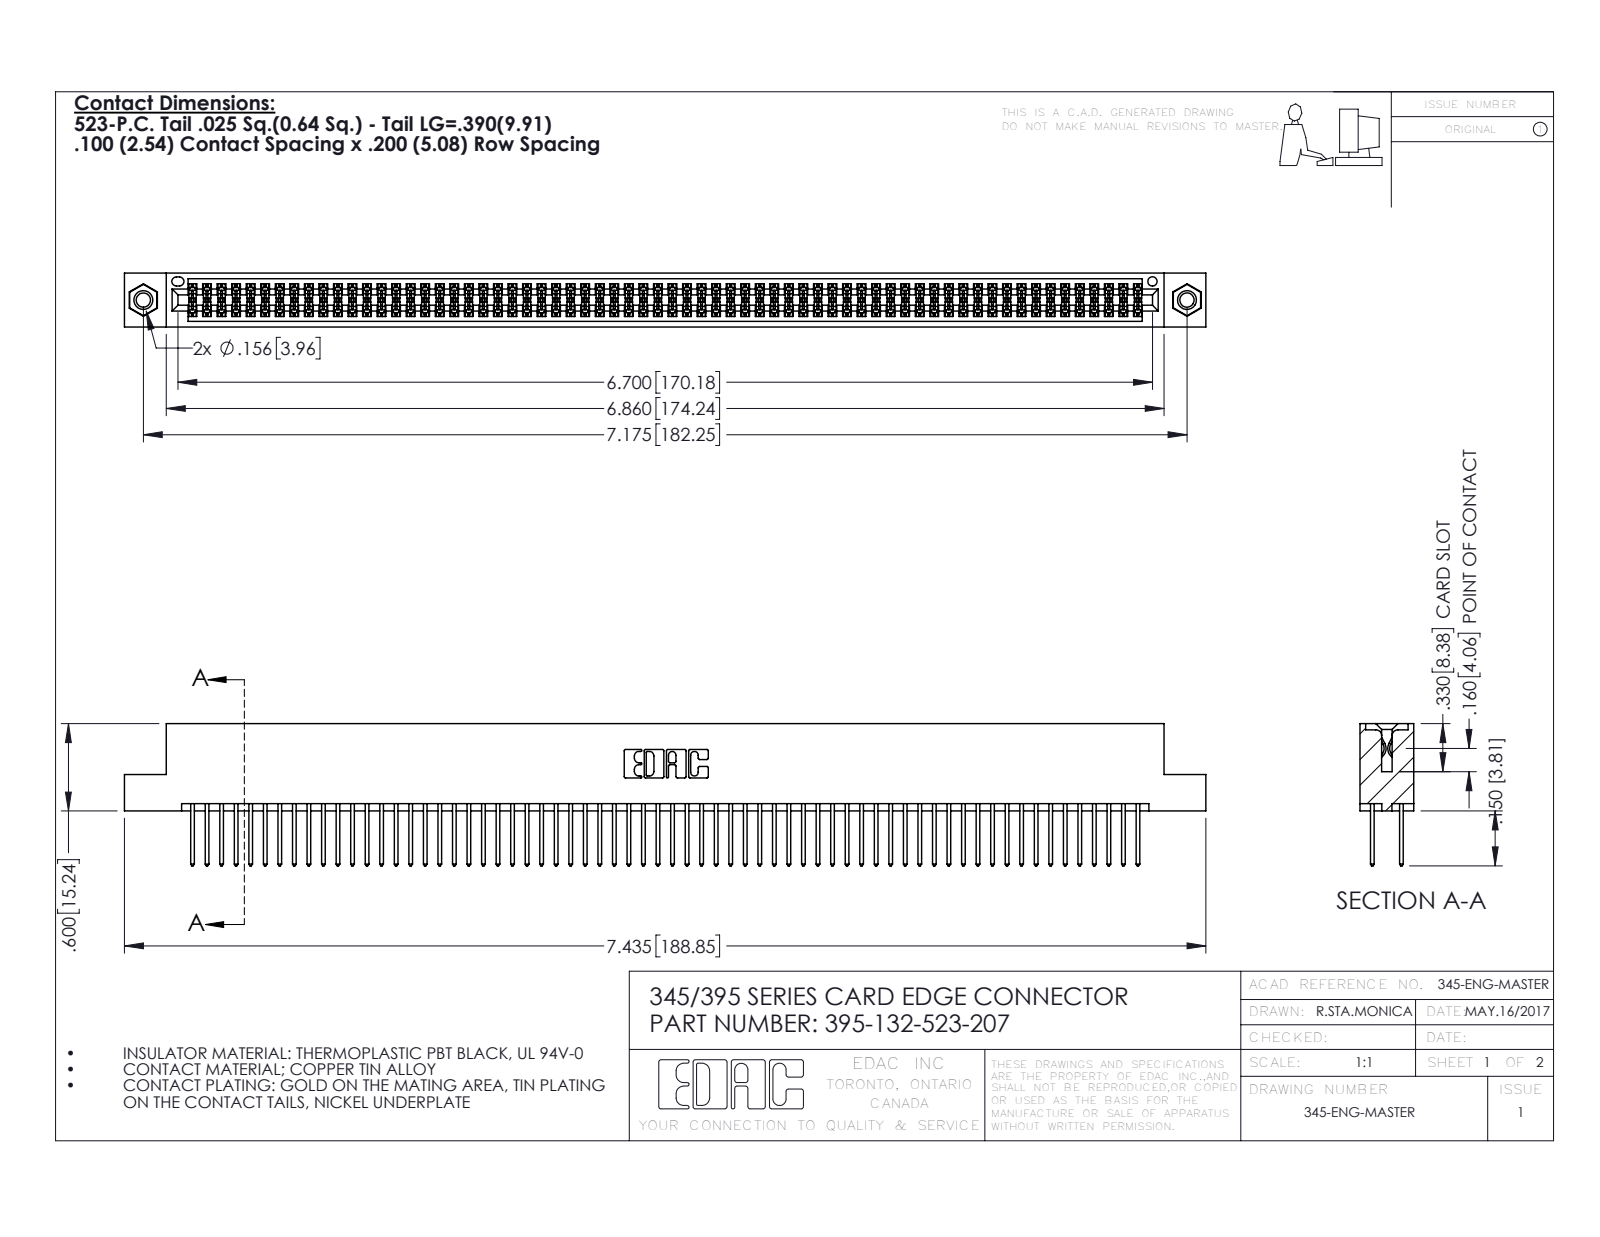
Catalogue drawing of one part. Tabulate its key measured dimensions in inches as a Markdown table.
| quantity | value |
| --- | --- |
| part name | 345-292-001_345-293-123; 345 Part_Flush Mounting Lugs - 0.156 Dia-TI; 395-132-523-207; 345-250-001_345-250-005-103 |
| STEP written by | SolidWorks 2016 (CONFIG_CONTROL_DESIGN) |
| units | inches |
| bodies | 135 solids, 6786 faces (4468 planar, 2302 cylindrical, 16 other) |
| overall size | 7.435 × 0.977 × 0.37 |
| volume | 1.149 in³ |
| surface area | 45.78 in² |
| round holes (diameter × count) | 0.098 × 2, 0.125 × 2, 0.156 × 2, 0.064 × 1 |
| round bosses / shafts (diameter × count) | 0.155 × 2 |
| partial cylindrical surfaces (radius × count) | 0.006 × 198, 0.01 × 132, 0.01 × 22, 0.007 × 6, 0.031 × 6, 0.026 × 3, 0.014 × 2, 0.019 × 2 |
| main face-to-face distances | 0.072, 0.298, 0.2, 0.098, 0.272, 0.025, 0.37, 0.225, 0.175, 0.149 |
| hole center spacings | 0.27, 6.939, 7.175 |
